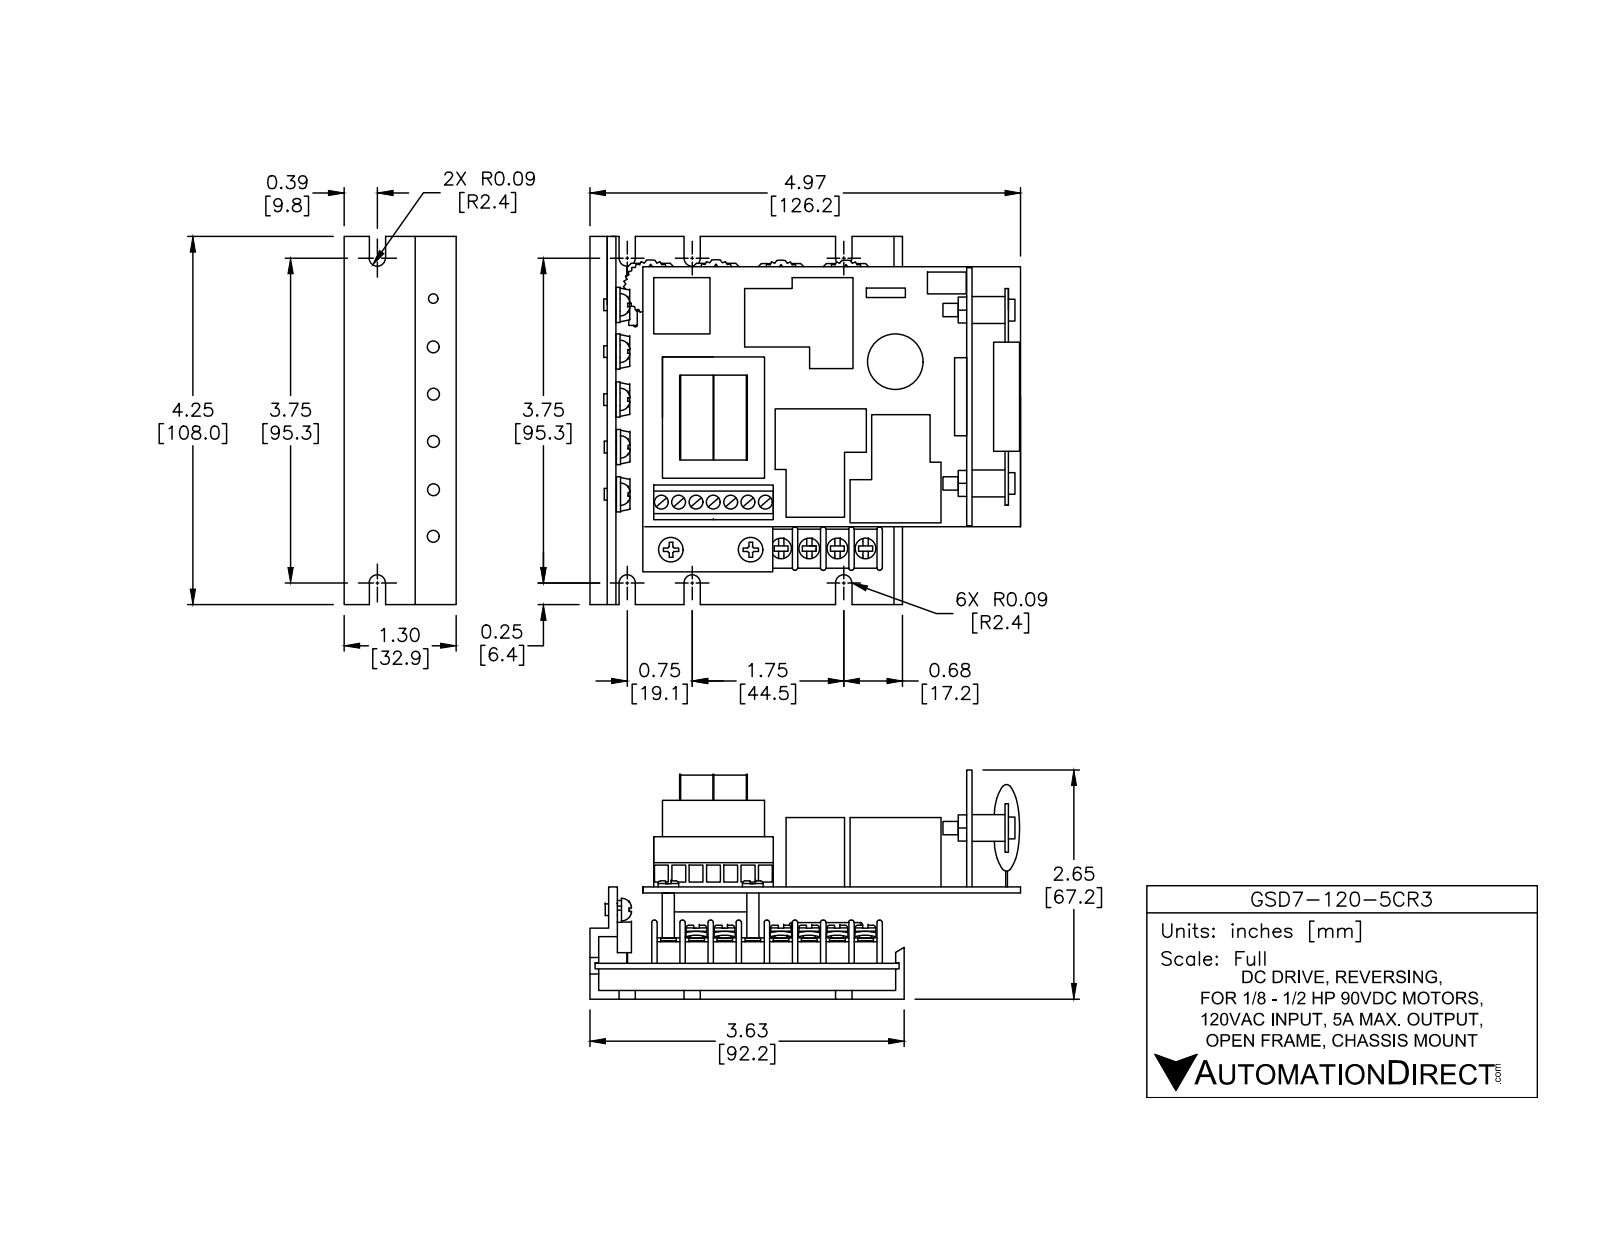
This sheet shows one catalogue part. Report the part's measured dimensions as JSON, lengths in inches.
{"part_name": "GSD7-120-5CR3; C9; CAP_AXIAL_16.51S-4D-4.1H; TH_CAP_AXIAL_19.050S-12L-5.25D-5.35H (+8 more)", "step_written_by": "SolidWorks 2014 (AUTOMOTIVE_DESIGN)", "units": "inches", "bodies": {"solids": 99, "faces": 5316, "planar": 2781, "cylindrical": 1893, "other": 642}, "overall_size": [5.227, 4.25, 2.527], "volume_in3": 11.08, "surface_area_in2": 213.3, "round_holes": [[0.033, 90], [0.043, 19], [0.035, 16], [0.046, 12], [0.07, 9], [0.035, 8], [0.09, 7], [0.147, 7], [0.04, 6], [0.11, 6], [0.144, 5], [0.111, 4]], "round_bosses_or_shafts": [[0.025, 43], [0.024, 30], [0.025, 22], [0.107, 20], [0.081, 19], [0.08, 19], [0.03, 16], [0.019, 12]], "partial_cylinders_radius": [[0.005, 23], [0.02, 12], [0.062, 12], [0.04, 11], [0.024, 10], [0.075, 8], [0.094, 8], [0.05, 6]], "face_to_face_distances": [0.1, 0.065, 1.127, 1.227, 0.25, 0.312, 0.75, 1.062, 1.162, 0.815], "hole_center_spacings": [0.2, 0.55, 0.1, 0.4, 0.461, 0.751, 0.636, 0.8]}
